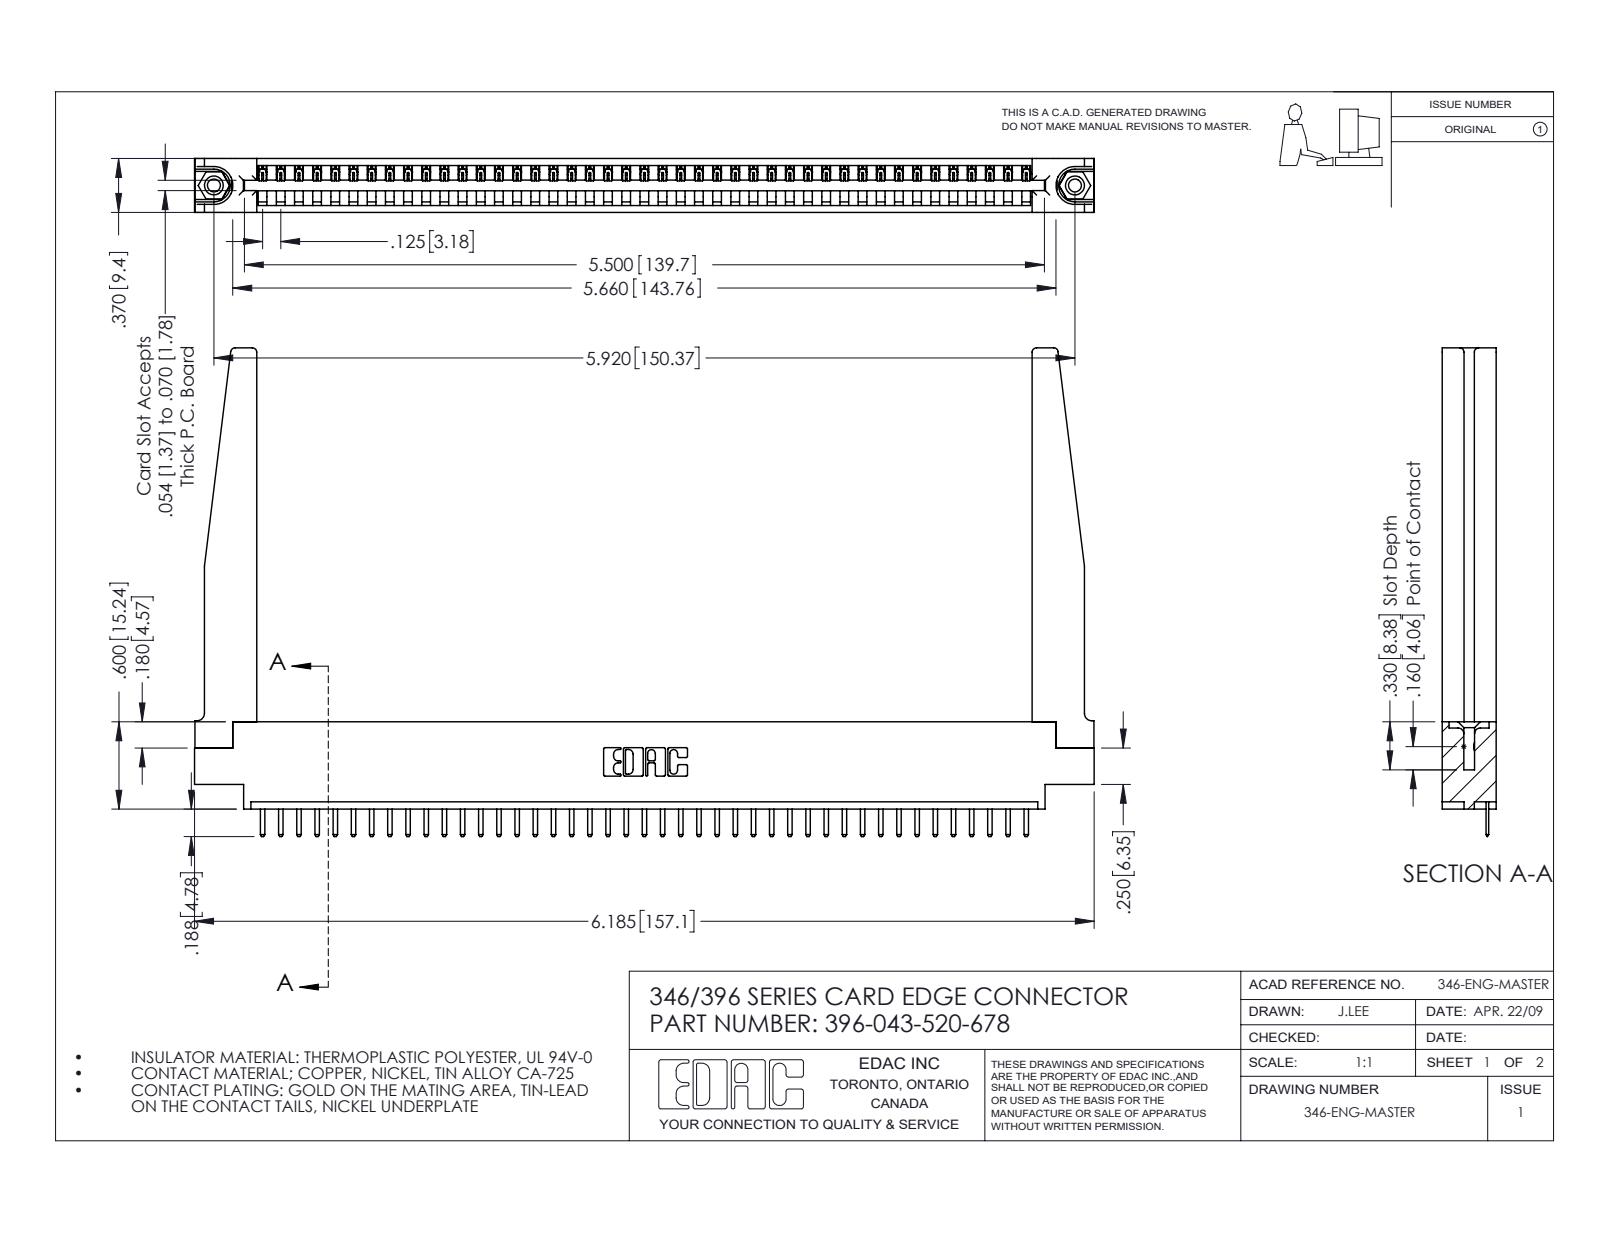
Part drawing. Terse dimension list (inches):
name: 345-292-001_345-293-120; 345-250-001_345-250-001-102; 346-220-078_345-220-078; 396-043-520-678 (+1 more)
written by: SolidWorks 2016 (CONFIG_CONTROL_DESIGN)
unit: in
bodies: 48 solids, 3026 faces (2028 planar, 946 cylindrical, 52 other)
size: 6.185 × 3.358 × 0.37
volume: 1.323 in³; area: 38.37 in²
holes: 2× ⌀0.089, 2× ⌀0.125, 2× ⌀0.156, 1× ⌀0.064
bosses: 2× ⌀0.155
rounds: 88× R0.01, 86× R0.006, 22× R0.01, 8× R0.03, 6× R0.007, 6× R0.031, 3× R0.026, 2× R0.031
face distances: 0.37, 0.048, 0.322, 0.148, 0.072, 0.15, 0.25, 0.222, 0.1, 0.174
hole spacings: 0.246, 5.711, 5.92
